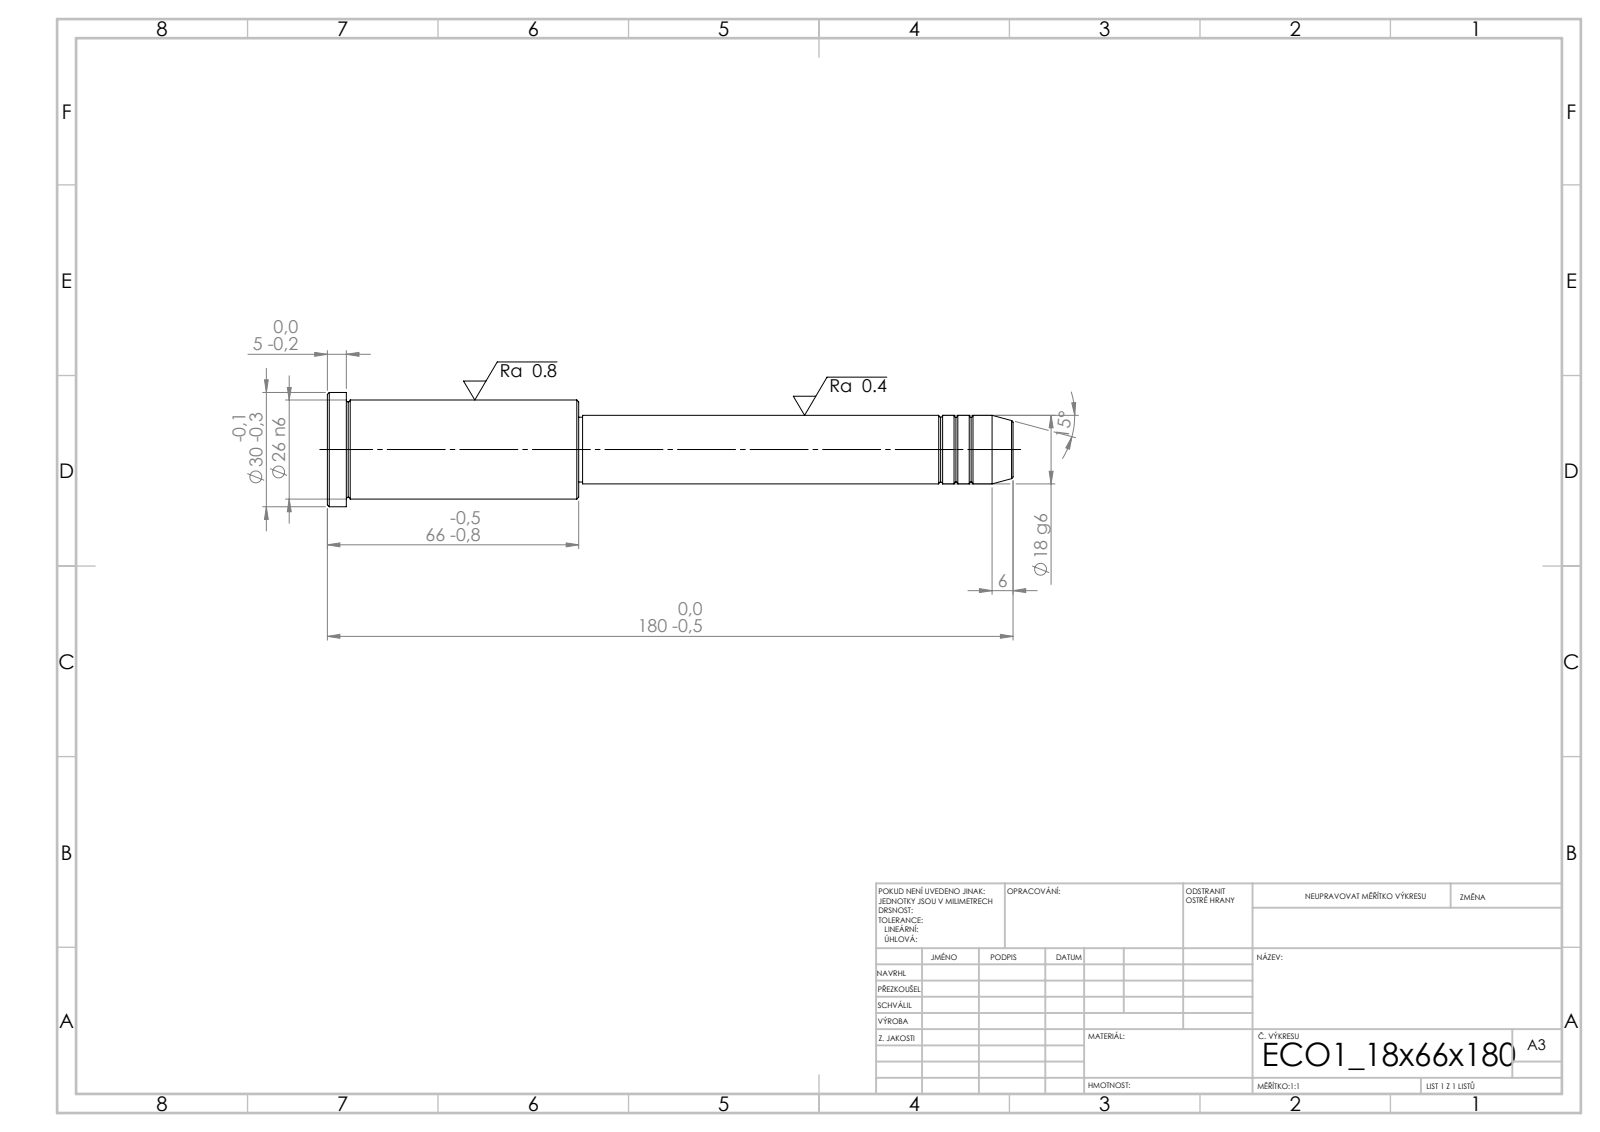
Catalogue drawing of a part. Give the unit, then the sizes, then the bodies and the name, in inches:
Units: inches
Overall size (bounding box): 7.087 × 1.181 × 1.181
Round bosses / shafts (diameter × count): ⌀1.181 ×1, ⌀1.024 ×1, ⌀0.709 ×1, ⌀0.669 ×1
Main face-to-face distances: 2.598, 2.402, 0.197, 4.488, 6.89, 7.087, 4.449, 0.039, 2.441, 2.638
Volume: 3.94 in³ · Surface area: 20.69 in²
Bodies: 1 solid, 43 faces (5 planar, 14 cylindrical, 24 other)
STEP written by: SolidWorks 2019 (CONFIG_CONTROL_DESIGN)
